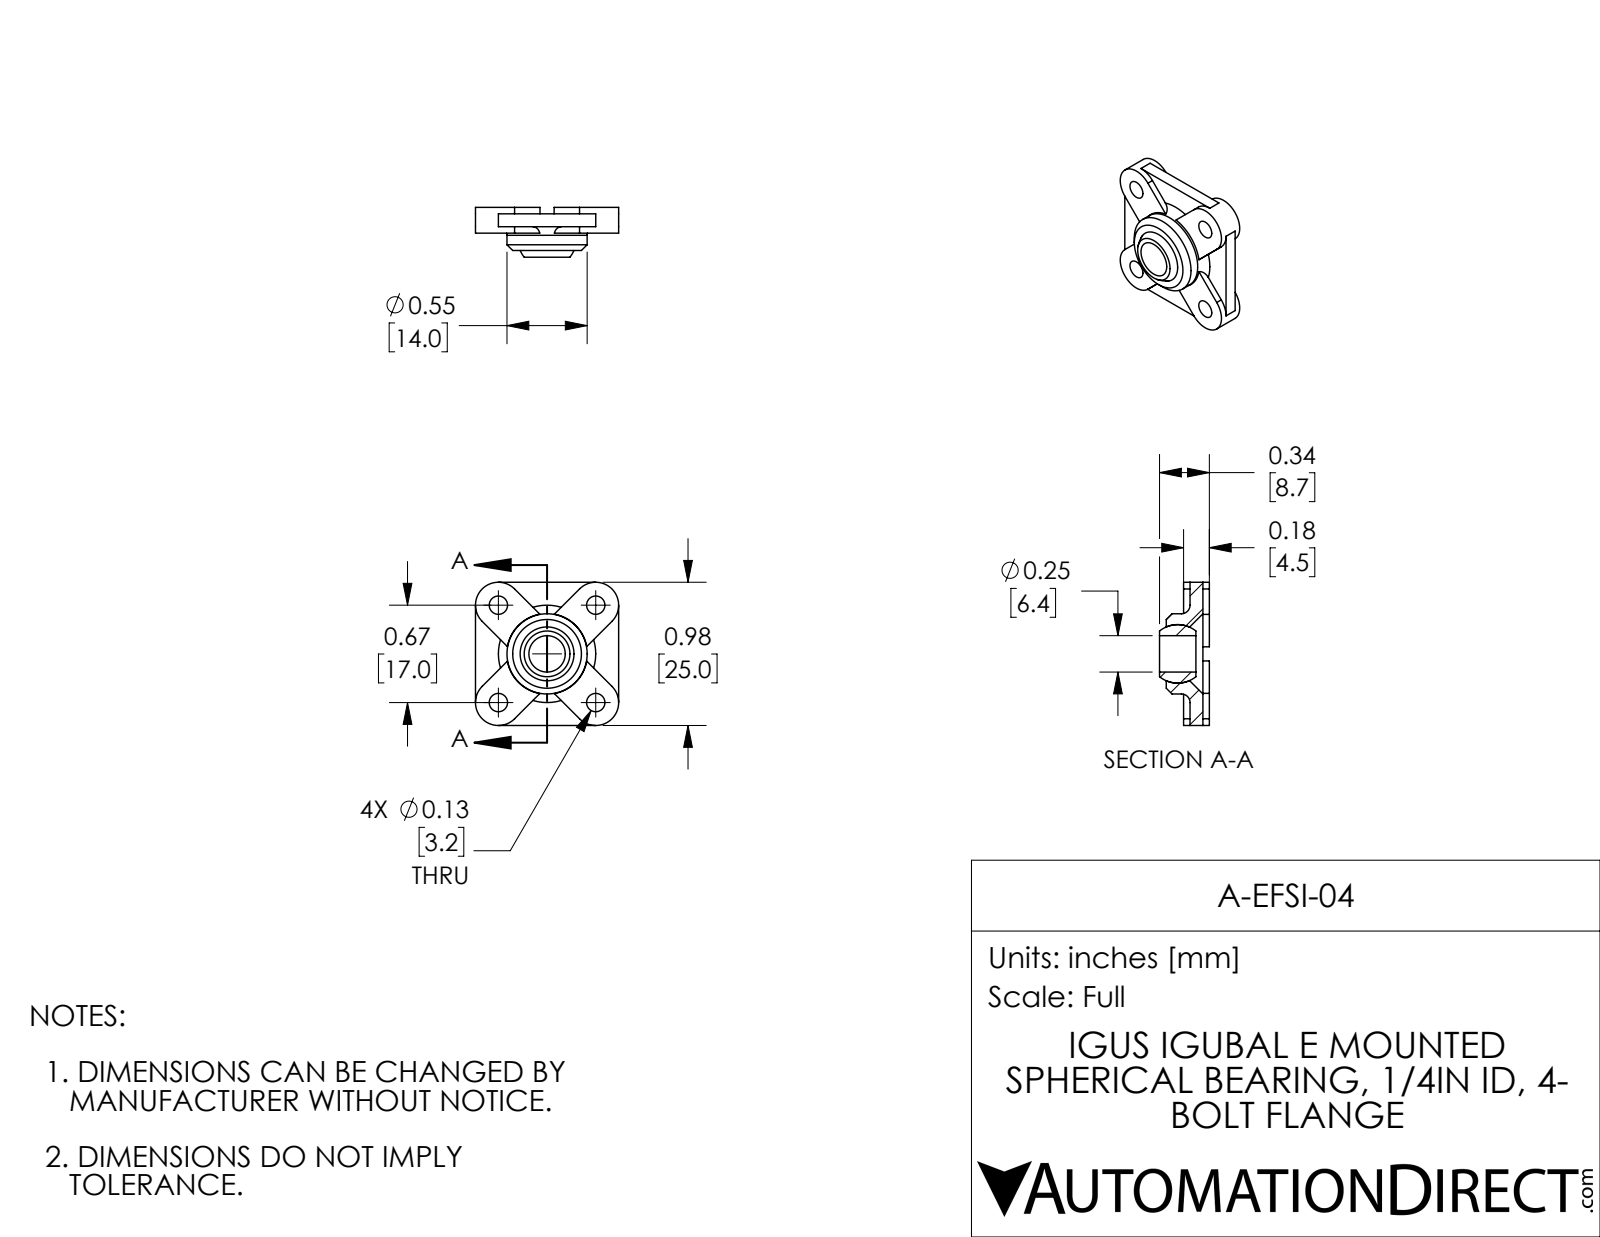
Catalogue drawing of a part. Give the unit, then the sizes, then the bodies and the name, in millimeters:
Units: millimetres
Overall size (bounding box): 25 × 25 × 10.4
Round holes (diameter × count): ⌀3.2 ×4, ⌀6.4 ×1, ⌀14 ×1
Partial cylindrical surfaces — rounded edges, fillets, slot ends (radius × count): R4 ×4
Main face-to-face distances: 1.1, 3.4, 4.5, 2.3, 25, 8, 7.5, 6.4, 4.1, 3
Hole centre spacings: 12, 17, 24
Volume: 2 150 mm³ · Surface area: 2 314 mm²
Bodies: 2 solids, 73 faces (39 planar, 24 cylindrical, 10 other)
Part name (STEP PRODUCT): A-EFSI-04
STEP written by: SolidWorks 2017 (AUTOMOTIVE_DESIGN)
